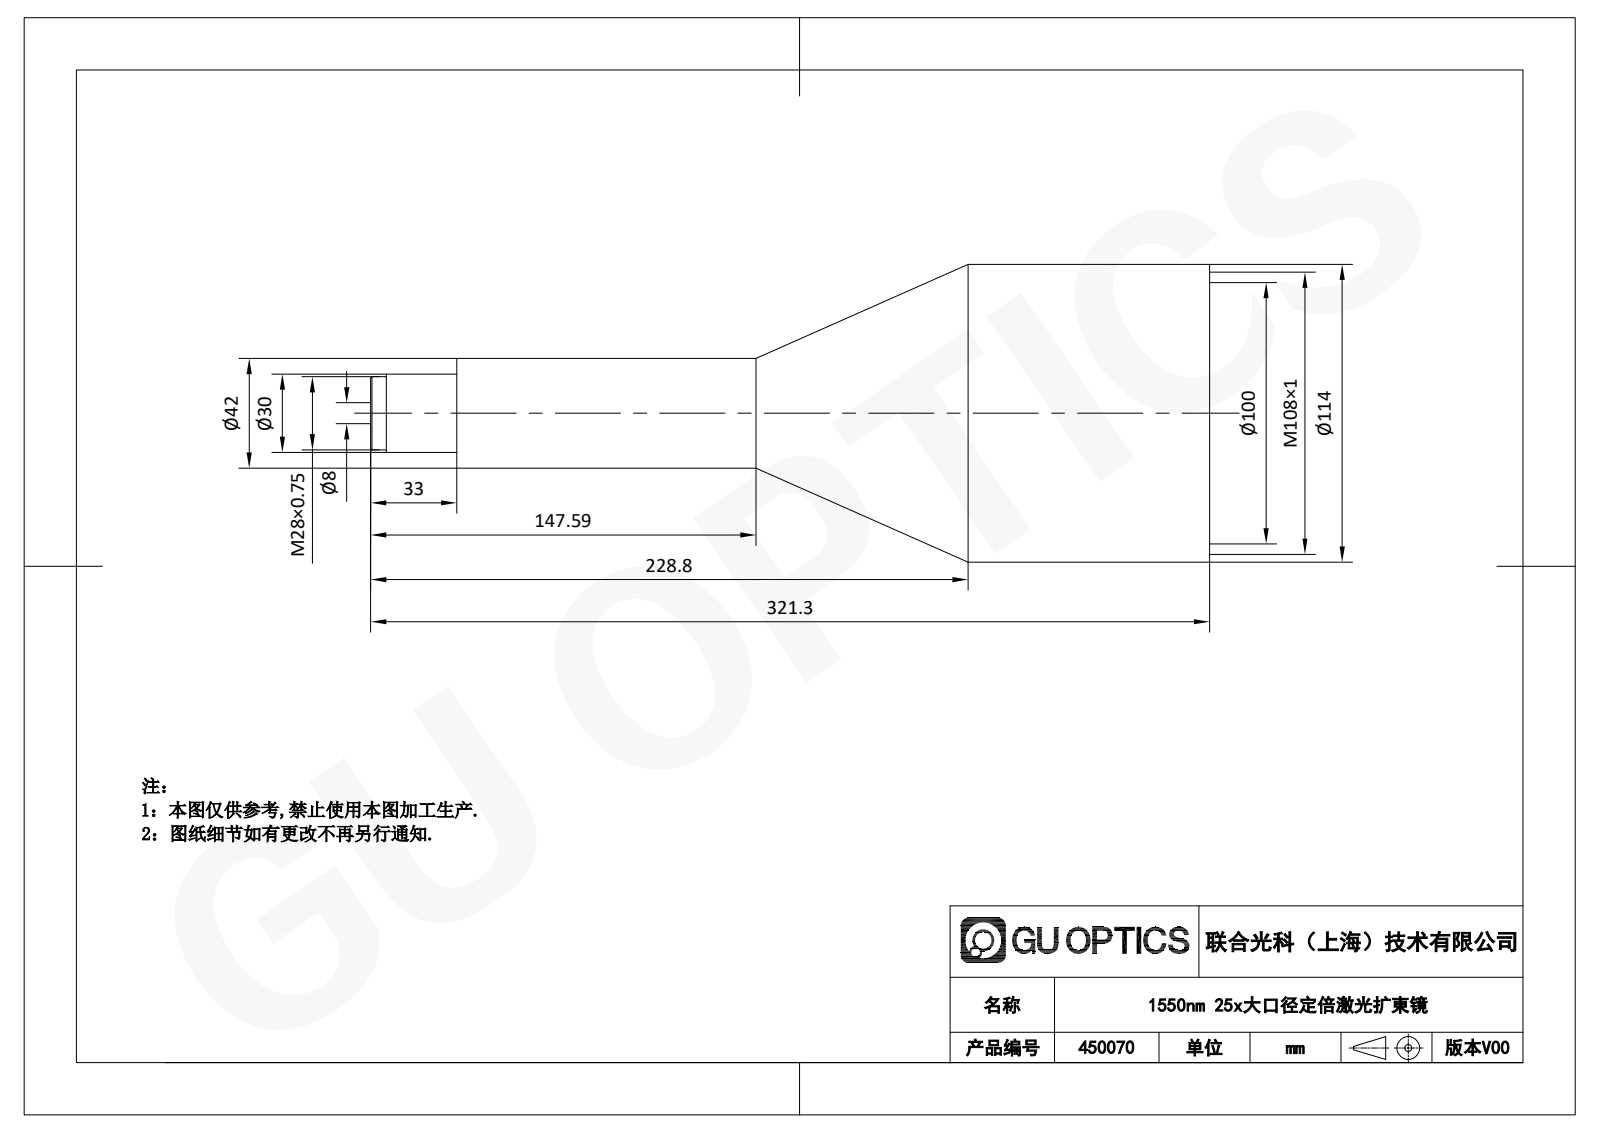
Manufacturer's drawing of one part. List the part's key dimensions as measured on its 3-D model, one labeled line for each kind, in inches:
Part name (STEP PRODUCT): 450070
STEP written by: SolidWorks 2020 (AUTOMOTIVE_DESIGN)
Units: inches
Bodies: 1 solid, 25 faces (7 planar, 14 cylindrical, 4 other)
Overall size (bounding box): 12.65 × 4.488 × 4.488
Volume: 93.98 in³ · Surface area: 132.3 in²
Round holes (diameter × count): ⌀0.315 ×1, ⌀4.252 ×1
Round bosses / shafts (diameter × count): ⌀4.488 ×1, ⌀3.937 ×1, ⌀1.654 ×1, ⌀1.181 ×1, ⌀1.102 ×1
Main face-to-face distances: 0.039, 11.311, 11.35, 12.61, 1.299, 12.65, 0.236, 1.063, 12.374, 12.413
